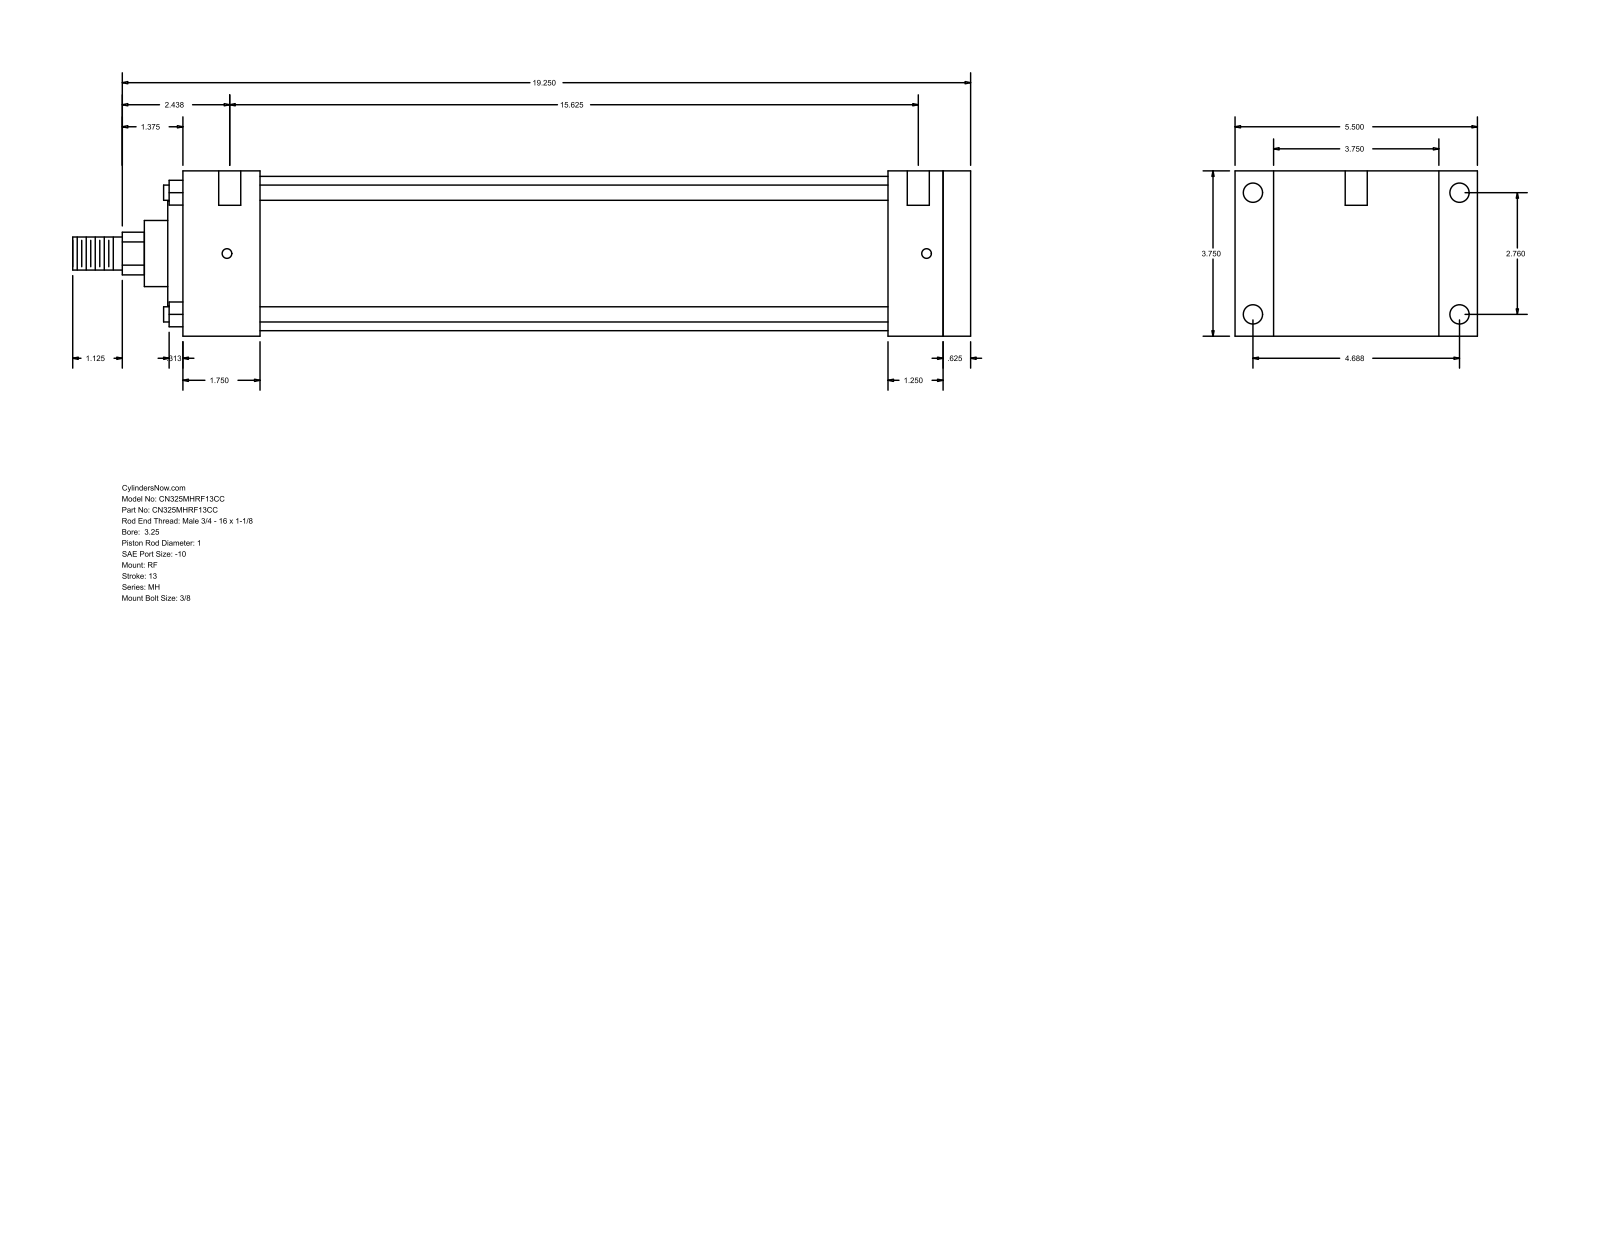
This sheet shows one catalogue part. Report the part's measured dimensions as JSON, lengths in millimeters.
{"part_name": "MH_RF__0325_1", "step_written_by": "GSSL Pune (CONFIG_CONTROL_DESIGN)", "units": "millimeters", "bodies": {"solids": 0, "faces": 94, "planar": 65, "cylindrical": 29, "other": 0}, "overall_size": [517.52, 139.7, 95.25], "round_holes": [[5.56, 4], [11.13, 4], [12.7, 2]], "round_bosses_or_shafts": [[8.76, 4], [88.9, 1], [60.33, 1], [38.1, 1], [25.4, 1], [19.05, 1]], "partial_cylinders_radius": [[12.29, 1]], "face_to_face_distances": [95.24, 454.03, 438.15, 15.88, 22.23, 117.47, 44.46, 393.69, 409.57, 406.4], "hole_center_spacings": [70.1, 119.06, 138.16, 403.22, 1.58, 4.76, 396.88, 398.46]}
